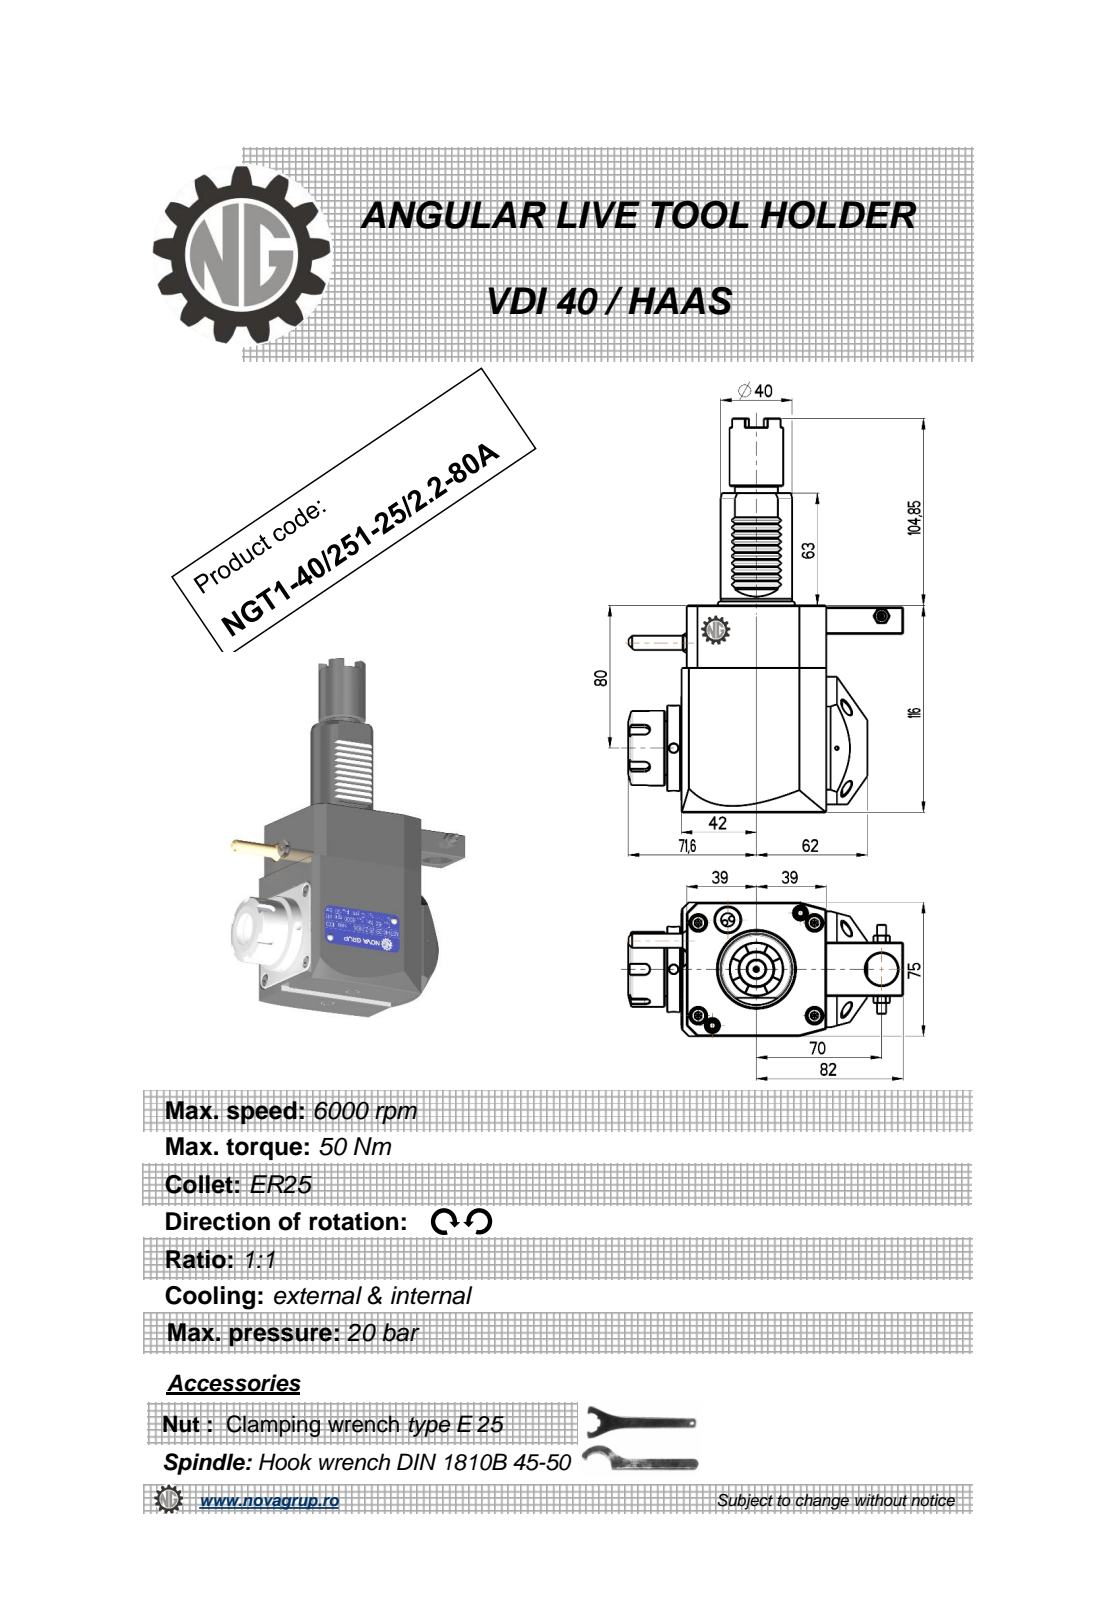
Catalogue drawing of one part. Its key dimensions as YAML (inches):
part_name: "NGT1_40_251_25_2_2_80A"
step_written_by: "PRO/ENGINEER BY PARAMETRIC TECHNOLOGY CORPORATION, 2010280 (CONFIG_CONTROL_DESIGN)"
units: inches
bodies: {solids: 1, faces: 476, planar: 223, cylindrical: 94, other: 159}
overall_size: [8.695, 6.047, 3.016]
volume: 55.28
surface_area: 117.5
round_holes:
  - {diameter: 0.197, count: 3}
  - {diameter: 0.118, count: 1}
  - {diameter: 0.165, count: 1}
  - {diameter: 0.374, count: 1}
  - {diameter: 0.709, count: 1}
  - {diameter: 0.799, count: 1}
round_bosses_or_shafts:
  - {diameter: 1.89, count: 1}
  - {diameter: 1.654, count: 1}
  - {diameter: 1.575, count: 1}
  - {diameter: 1.476, count: 1}
  - {diameter: 1.299, count: 1}
  - {diameter: 1.181, count: 1}
  - {diameter: 0.945, count: 1}
  - {diameter: 0.394, count: 1}
partial_cylinders:
  - {radius: 0.01, count: 12}
  - {radius: 0.012, count: 10}
  - {radius: 0.008, count: 6}
  - {radius: 0.118, count: 5}
  - {radius: 0.02, count: 1}
  - {radius: 0.384, count: 1}
  - {radius: 1.575, count: 1}
face_to_face_distances: [2.953, 4.567, 3.189, 0.118, 3.071, 0.11, 3.181, 0.039, 4.409, 0.433]
hole_center_spacings: [0.824, 2.407, 2.854, 4.577, 5.425]
